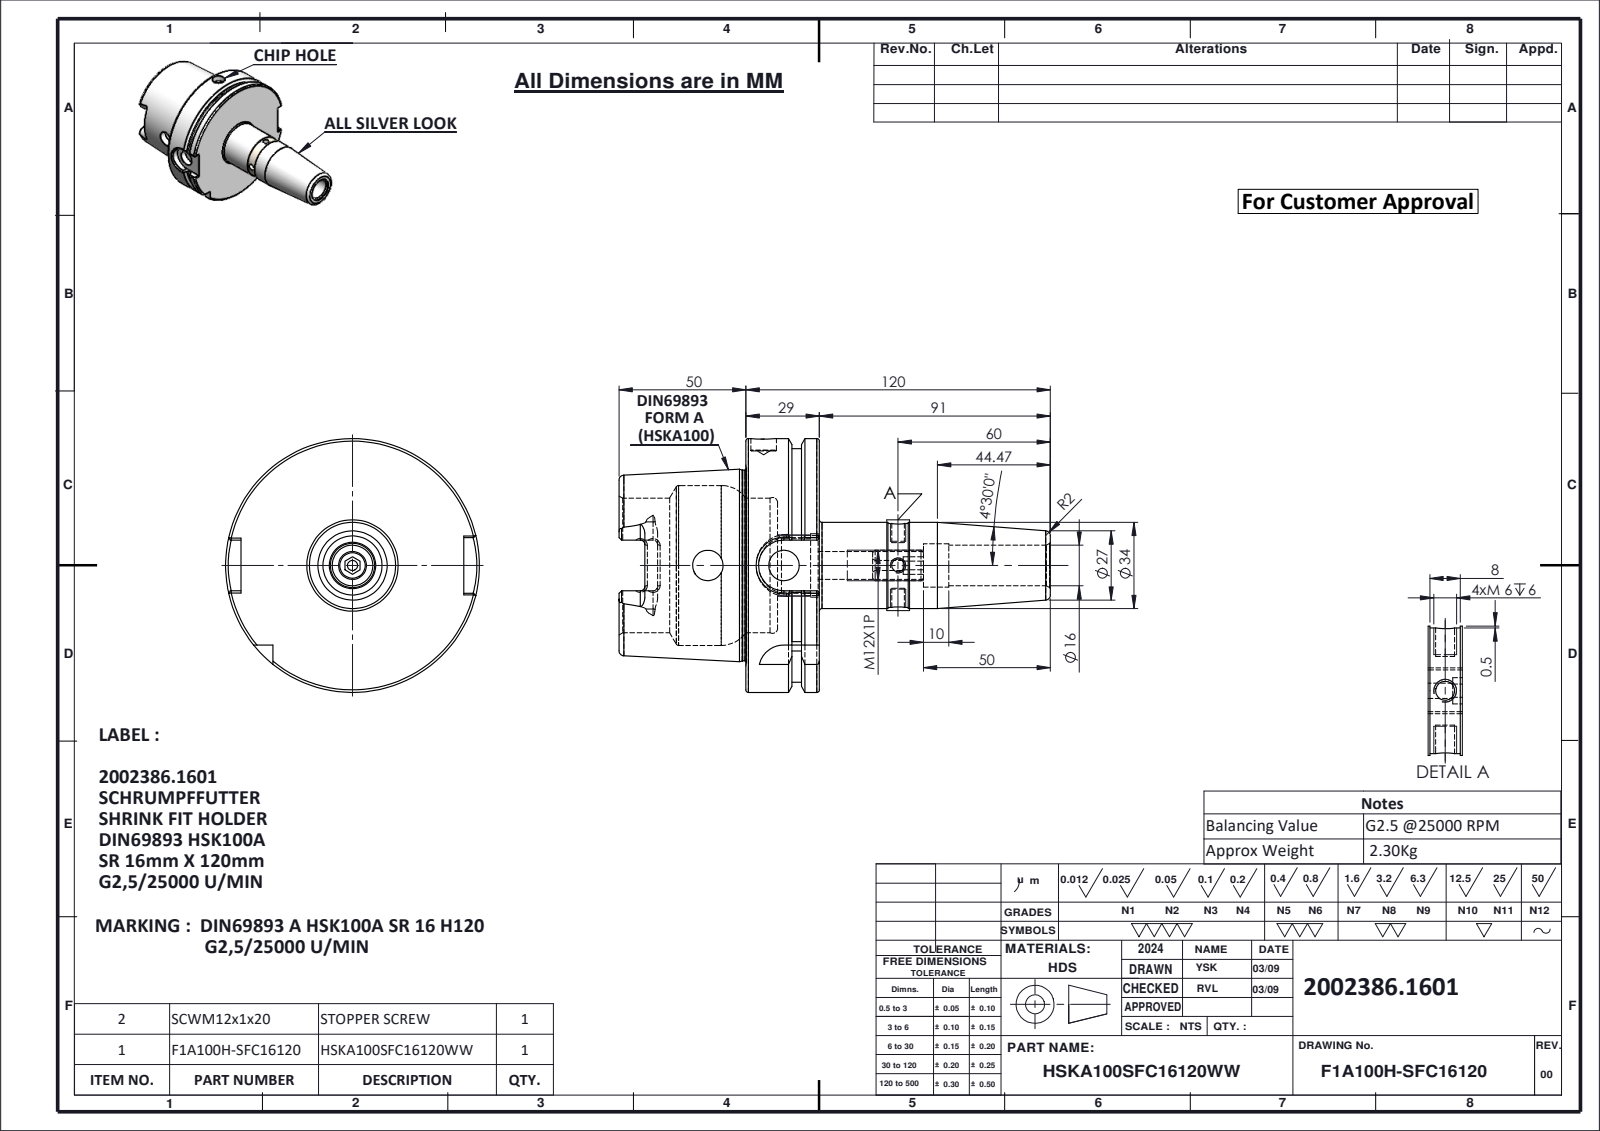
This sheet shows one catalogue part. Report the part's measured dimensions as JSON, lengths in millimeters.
{"part_name": "HSKA100SFC16120; F1A100H-SFC16120; SCWM12X1P", "step_written_by": "SolidWorks 2024 (CONFIG_CONTROL_DESIGN)", "units": "millimeters", "bodies": {"solids": 2, "faces": 214, "planar": 68, "cylindrical": 68, "other": 78}, "overall_size": [169.95, 100, 100], "volume_mm3": 315031, "surface_area_mm2": 64268, "round_holes": [[5, 2], [12, 2], [4, 1], [10, 1], [11, 1], [16, 1], [17, 1], [21, 1], [25, 1], [53, 1], [63, 1]], "round_bosses_or_shafts": [[100, 1], [92, 1], [75.16, 1], [34, 1], [33, 1], [12, 1]], "partial_cylinders_radius": [[1.8, 6], [4.88, 4], [10, 2], [11, 1]], "face_to_face_distances": [28.95, 12.5, 16.45, 50, 62.5, 78.95, 16, 71.88, 21.88, 9.38], "hole_center_spacings": [30, 44.95, 52.95, 74.95]}
